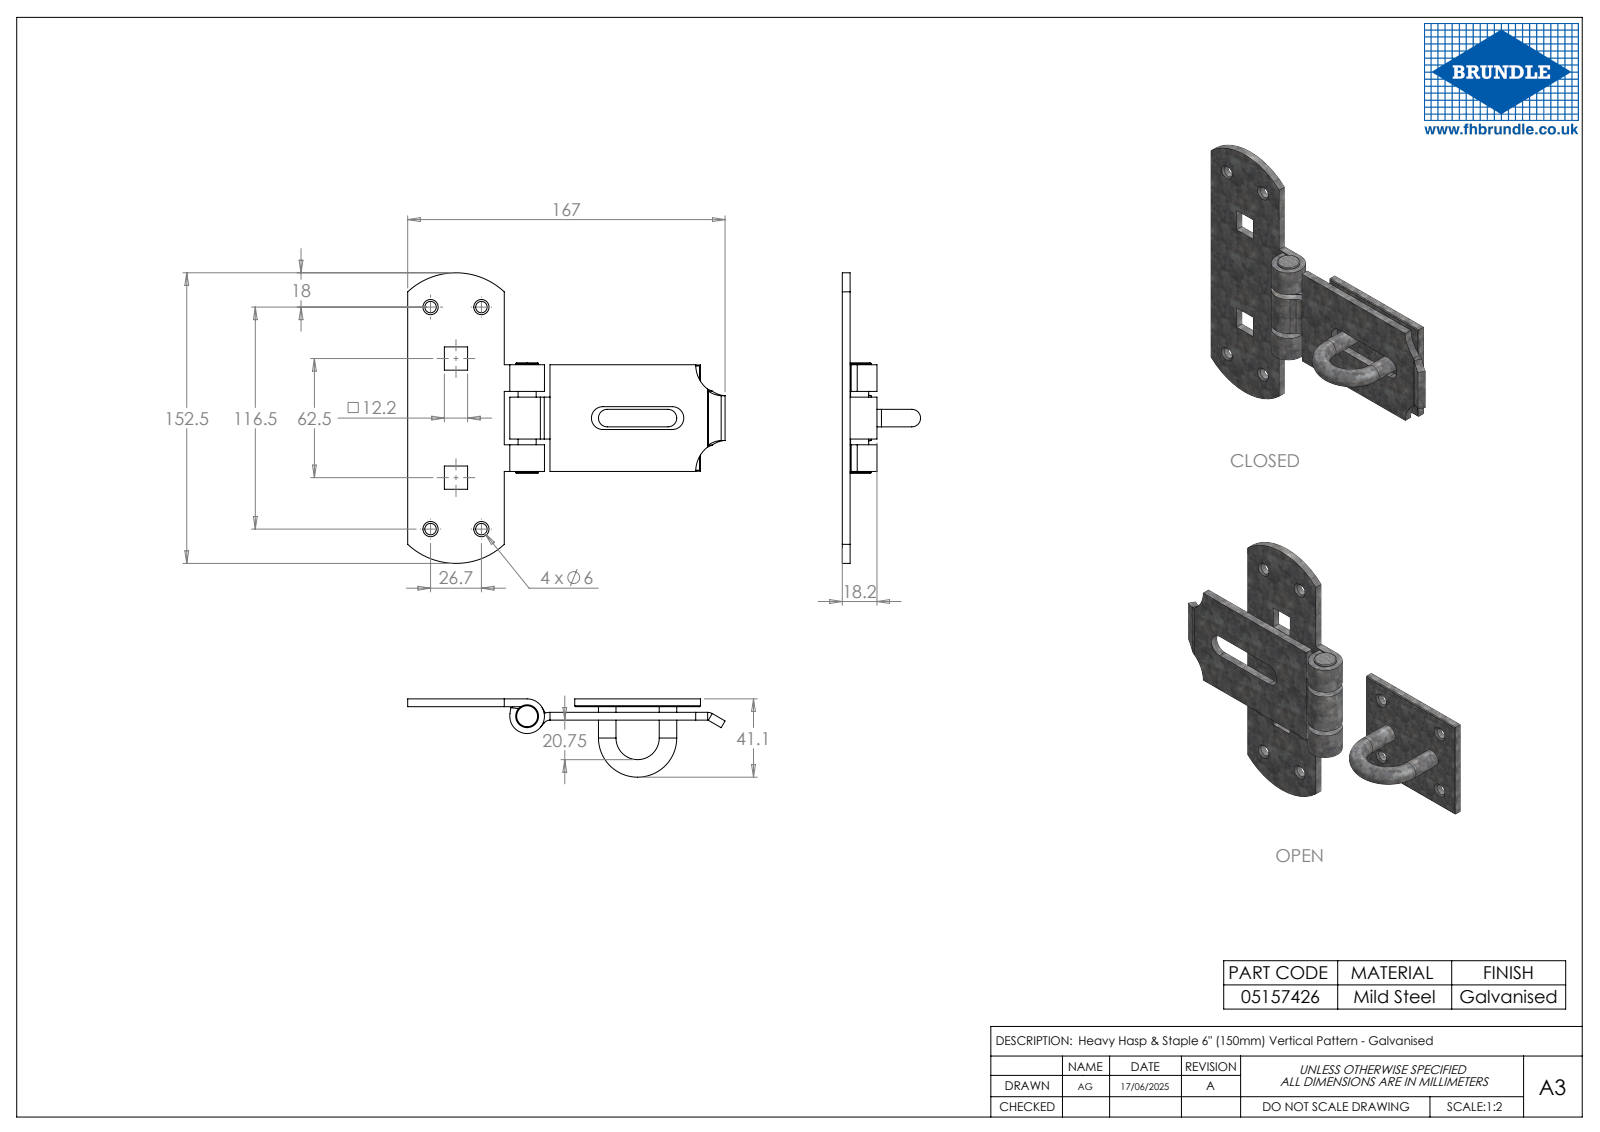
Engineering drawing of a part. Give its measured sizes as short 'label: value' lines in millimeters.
name: 05157426 Part4; 05157426 Part3; 05157426 Part2; 05157426 (+1 more)
written by: SolidWorks 2023 (CONFIG_CONTROL_DESIGN)
unit: mm
bodies: 5 solids, 132 faces (53 planar, 55 cylindrical, 24 other)
size: 166.62 × 152.5 × 41.1
volume: 80 155 mm³; area: 45 087 mm²
holes: 4× ⌀5.8, 4× ⌀6, 1× ⌀10
bosses: 2× ⌀9.2, 1× ⌀18.2, 1× ⌀12, 1× ⌀9.5
rounds: 4× R0.5, 4× R16.27, 2× R6, 2× R37.13, 1× R0.74, 1× R4, 1× R4.84, 1× R8
face distances: 4.1, 7.05, 11.15, 2.95, 17, 56, 22, 55.88, 50.7, 14
hole spacings: 26.7, 35.96, 43.2, 56.21, 72.59, 95.96, 97.26, 111.15
